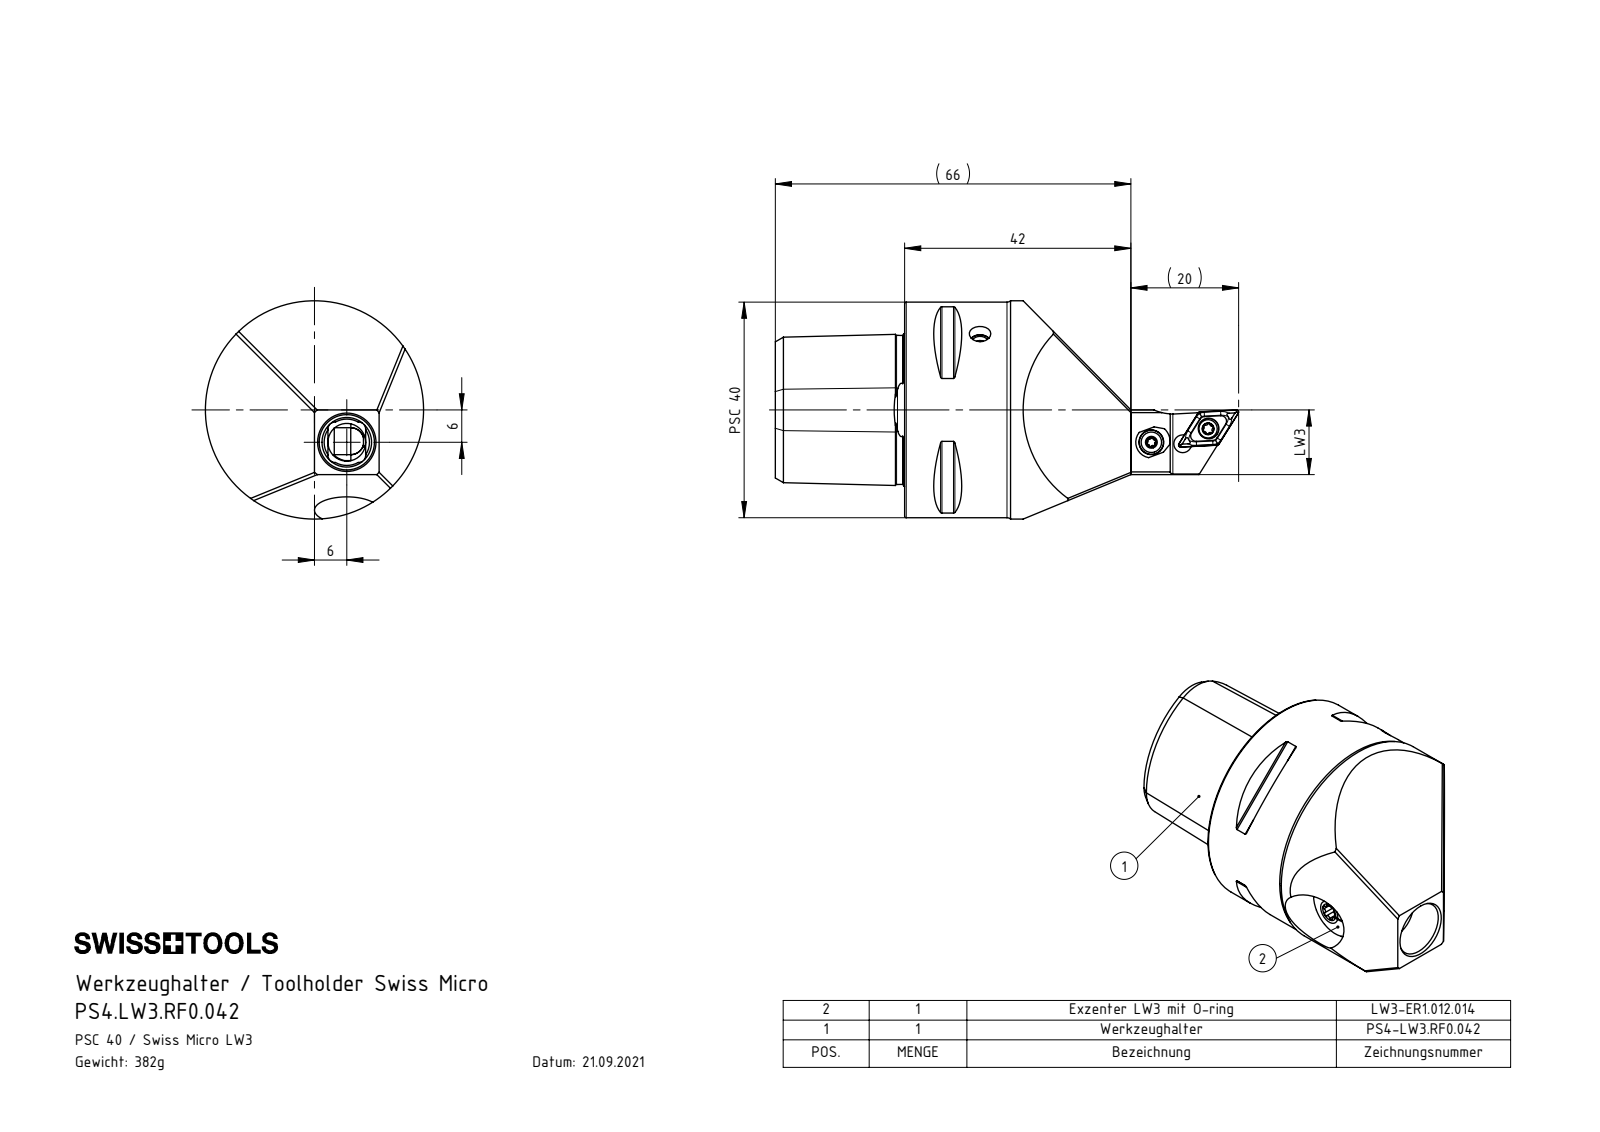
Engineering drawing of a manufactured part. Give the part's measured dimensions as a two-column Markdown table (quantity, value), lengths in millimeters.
| quantity | value |
| --- | --- |
| part name | KVT_MB_600_040; LW3-ER1.012.014; PS4.LW3.RF0.042; LW3-ER1.012.014_C_Standard<Wie bearbeitet> (+2 more) |
| STEP written by | SolidWorks 2017 (AUTOMOTIVE_DESIGN) |
| units | millimeters |
| bodies | 6 solids, 223 faces (65 planar, 66 cylindrical, 92 other) |
| overall size | 66 × 40.5 × 40.5 |
| volume | 46 079 mm³ |
| surface area | 12 671 mm² |
| round holes (diameter × count) | 3.3 × 2, 4 × 2, 1 × 1, 2.4 × 1, 3 × 1, 4.6 × 1, 7 × 1, 9.21 × 1, 12 × 1, 12.5 × 1, 18 × 1, 20 × 1 |
| round bosses / shafts (diameter × count) | 40.5 × 1, 40 × 1, 11.4 × 1, 9.5 × 1, 7.7 × 1, 4 × 1 |
| partial cylindrical surfaces (radius × count) | 0.3 × 8, 0.34 × 6, 0.59 × 6, 1.3 × 4, 2.5 × 2, 3 × 1, 3.6 × 1, 3.7 × 1 |
| main face-to-face distances | 24, 15.52, 35.3, 1.1, 15, 9, 12, 66, 51, 42 |
| hole center spacings | 8.49, 23.5 |
